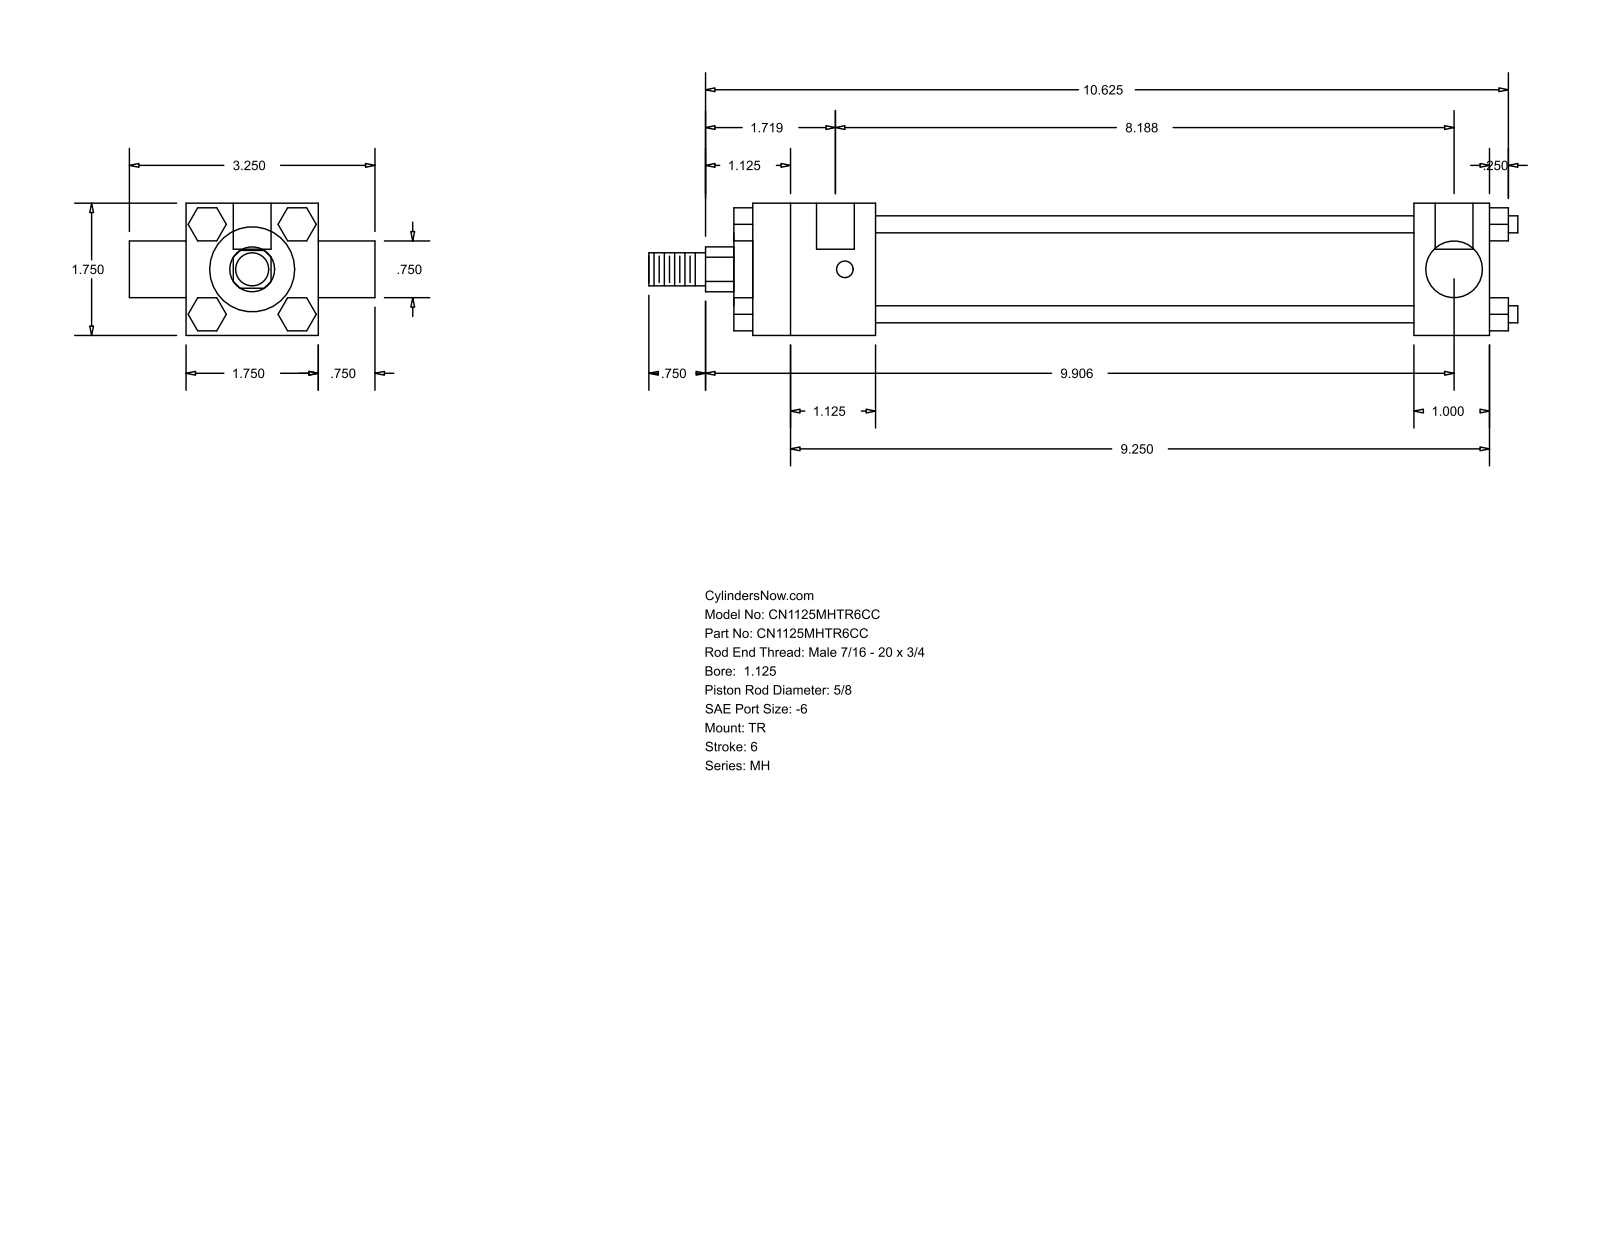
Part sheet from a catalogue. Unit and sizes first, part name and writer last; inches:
Units: inches
Overall size (bounding box): 11.5 × 3.25 × 1.75
Round holes (diameter × count): ⌀0.219 ×3, ⌀0.5 ×2
Round bosses / shafts (diameter × count): ⌀0.225 ×4, ⌀1.375 ×1, ⌀1.125 ×1, ⌀0.75 ×1, ⌀0.625 ×1, ⌀0.437 ×1
Partial cylindrical surfaces — rounded edges, fillets, slot ends (radius × count): R0.297 ×1
Main face-to-face distances: 1.75, 0.437, 1, 7.125, 8.125, 1.625, 8.75, 9.75, 1.875, 0.25
Hole centre spacings: 0.125, 8.063, 8.187
Bodies: 0 solids, 120 faces (92 planar, 28 cylindrical, 0 other)
Part name (STEP PRODUCT): MH_TR__0112_0.625
STEP written by: GSSL Pune (CONFIG_CONTROL_DESIGN)
